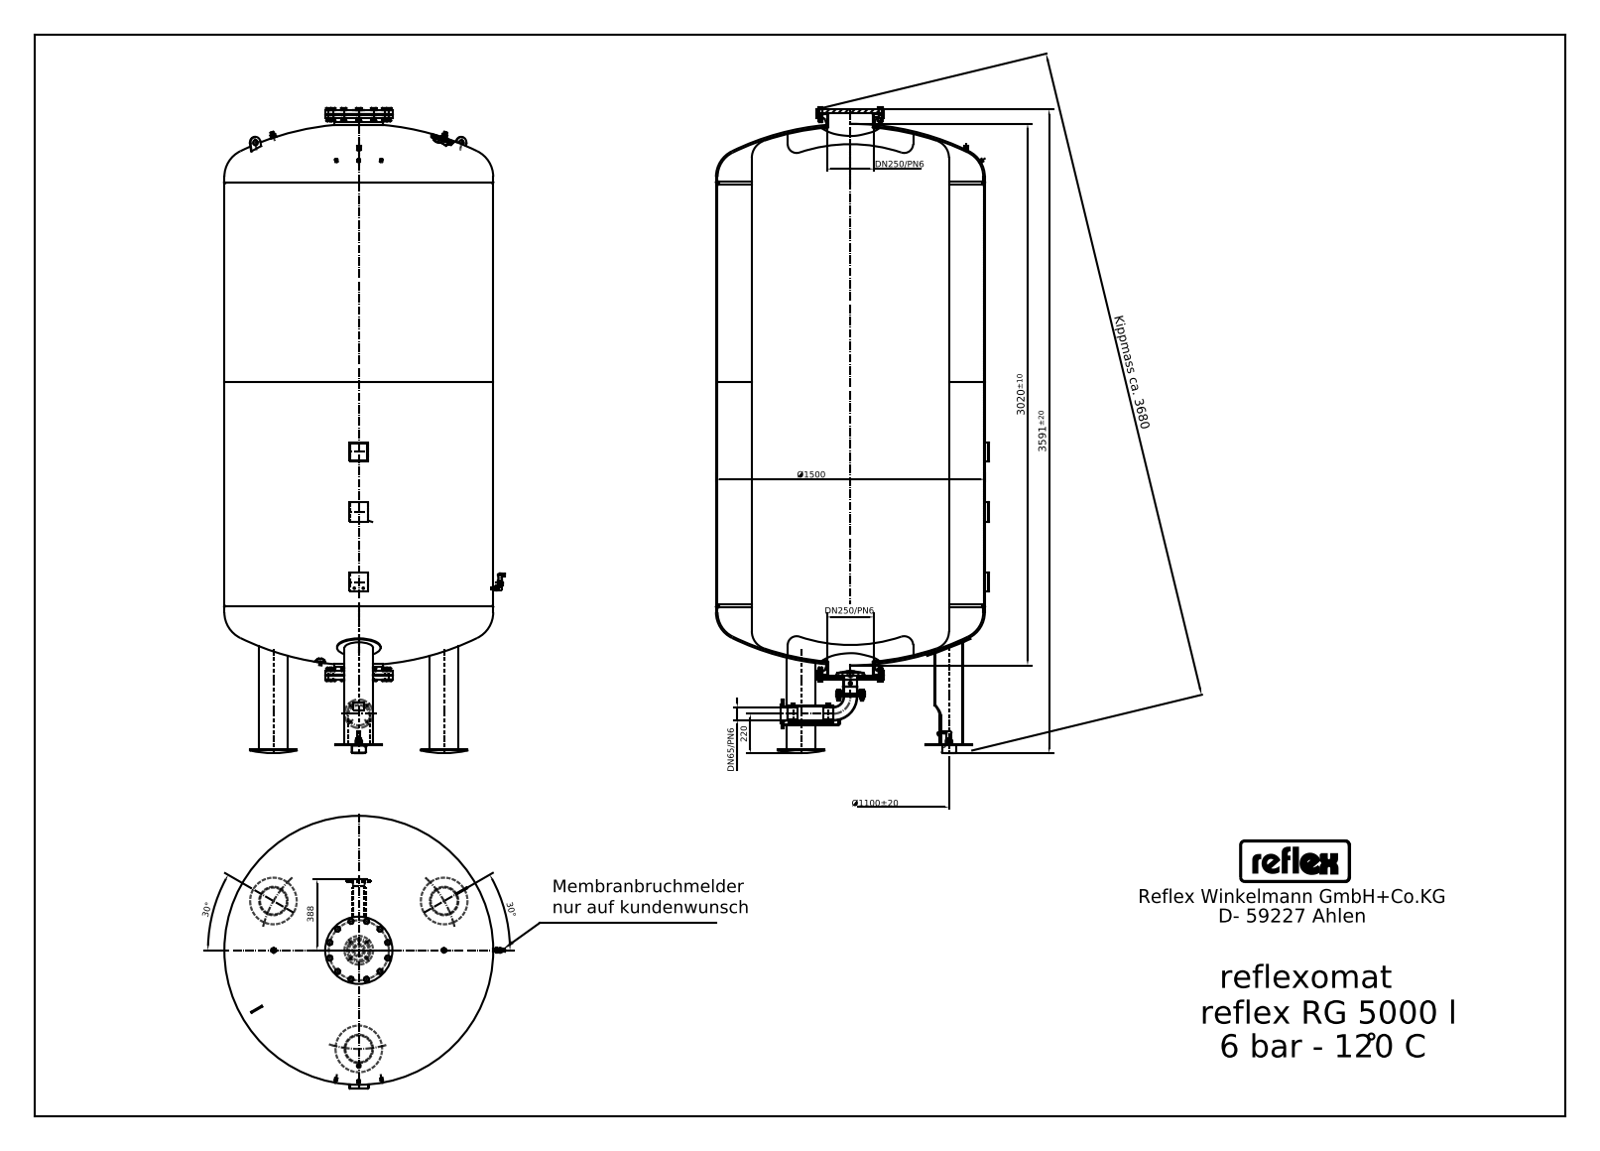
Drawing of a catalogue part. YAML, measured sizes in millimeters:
step_written_by: "Mechanical Desktop 2009 (CONFIG_CONTROL_DESIGN)"
units: millimeters
bodies: {solids: 33, faces: 1142, planar: 640, cylindrical: 270, other: 232}
overall_size: [3600, 1566, 1520]
volume: 5022000000
surface_area: 25930000
round_holes:
  - {diameter: 9, count: 2}
  - {diameter: 11.45, count: 2}
  - {diameter: 3.5, count: 1}
  - {diameter: 8, count: 1}
  - {diameter: 14.95, count: 1}
  - {diameter: 20, count: 1}
  - {diameter: 30, count: 1}
  - {diameter: 150, count: 1}
  - {diameter: 260.4, count: 1}
round_bosses_or_shafts:
  - {diameter: 16, count: 12}
  - {diameter: 12, count: 4}
  - {diameter: 159, count: 3}
  - {diameter: 21.3, count: 3}
  - {diameter: 18.5, count: 3}
  - {diameter: 76.1, count: 2}
  - {diameter: 28, count: 2}
  - {diameter: 20, count: 2}
partial_cylinders:
  - {radius: 2, count: 10}
  - {radius: 1, count: 5}
  - {radius: 8.44, count: 4}
  - {radius: 3.38, count: 3}
  - {radius: 6, count: 3}
  - {radius: 3, count: 2}
  - {radius: 5.76, count: 2}
  - {radius: 10.12, count: 2}
face_to_face_distances: [2360, 22, 3155, 27, 3128, 384, 2749, 389, 2771, 411]
hole_center_spacings: [820.38, 50, 95, 550, 645, 769.5, 945.85, 1004.07]
